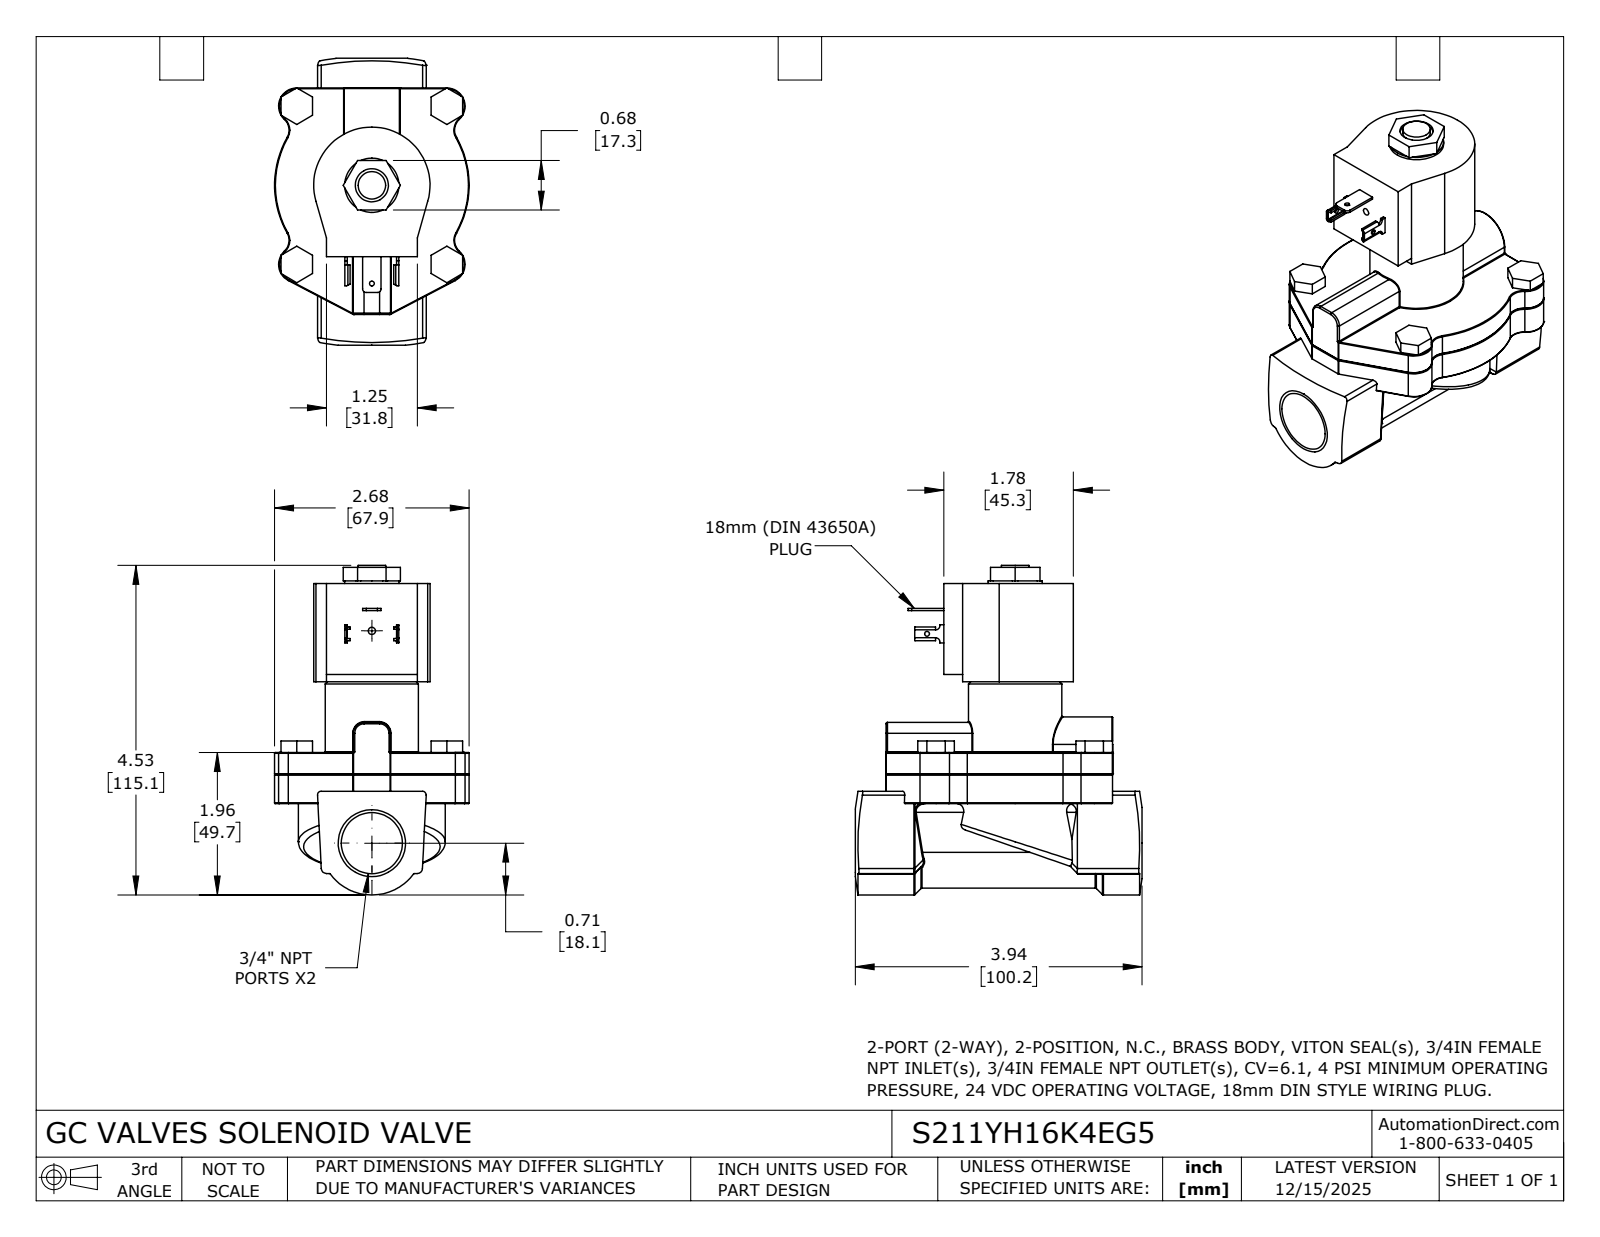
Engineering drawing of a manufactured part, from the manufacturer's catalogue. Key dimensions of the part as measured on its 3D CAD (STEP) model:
Part name (STEP PRODUCT): S211YH16K4EG5
STEP written by: SolidWorks 2024 (CONFIG_CONTROL_DESIGN)
Units: inches
Bodies: 1 solid, 443 faces (159 planar, 147 cylindrical, 137 other)
Overall size (bounding box): 4.531 × 3.944 × 2.675
Volume: 15.68 in³ · Surface area: 57.19 in²
Round holes (diameter × count): ⌀0.066 ×1, ⌀0.067 ×1, ⌀0.1 ×1, ⌀0.456 ×1, ⌀0.84 ×1
Round bosses / shafts (diameter × count): ⌀1.282 ×1, ⌀0.746 ×1, ⌀0.377 ×1
Partial cylindrical surfaces — rounded edges, fillets, slot ends (radius × count): R0.01 ×29, R0.02 ×14, R0.1 ×6, R0.006 ×4, R0.041 ×4, R0.05 ×4, R0.2 ×4, R0.25 ×4
Main face-to-face distances: 0.702, 3.025, 2.323, 0.17, 0.532, 2.855, 2.319, 1.675, 1.505, 0.973
Hole centre spacings: 1.35, 2.918
